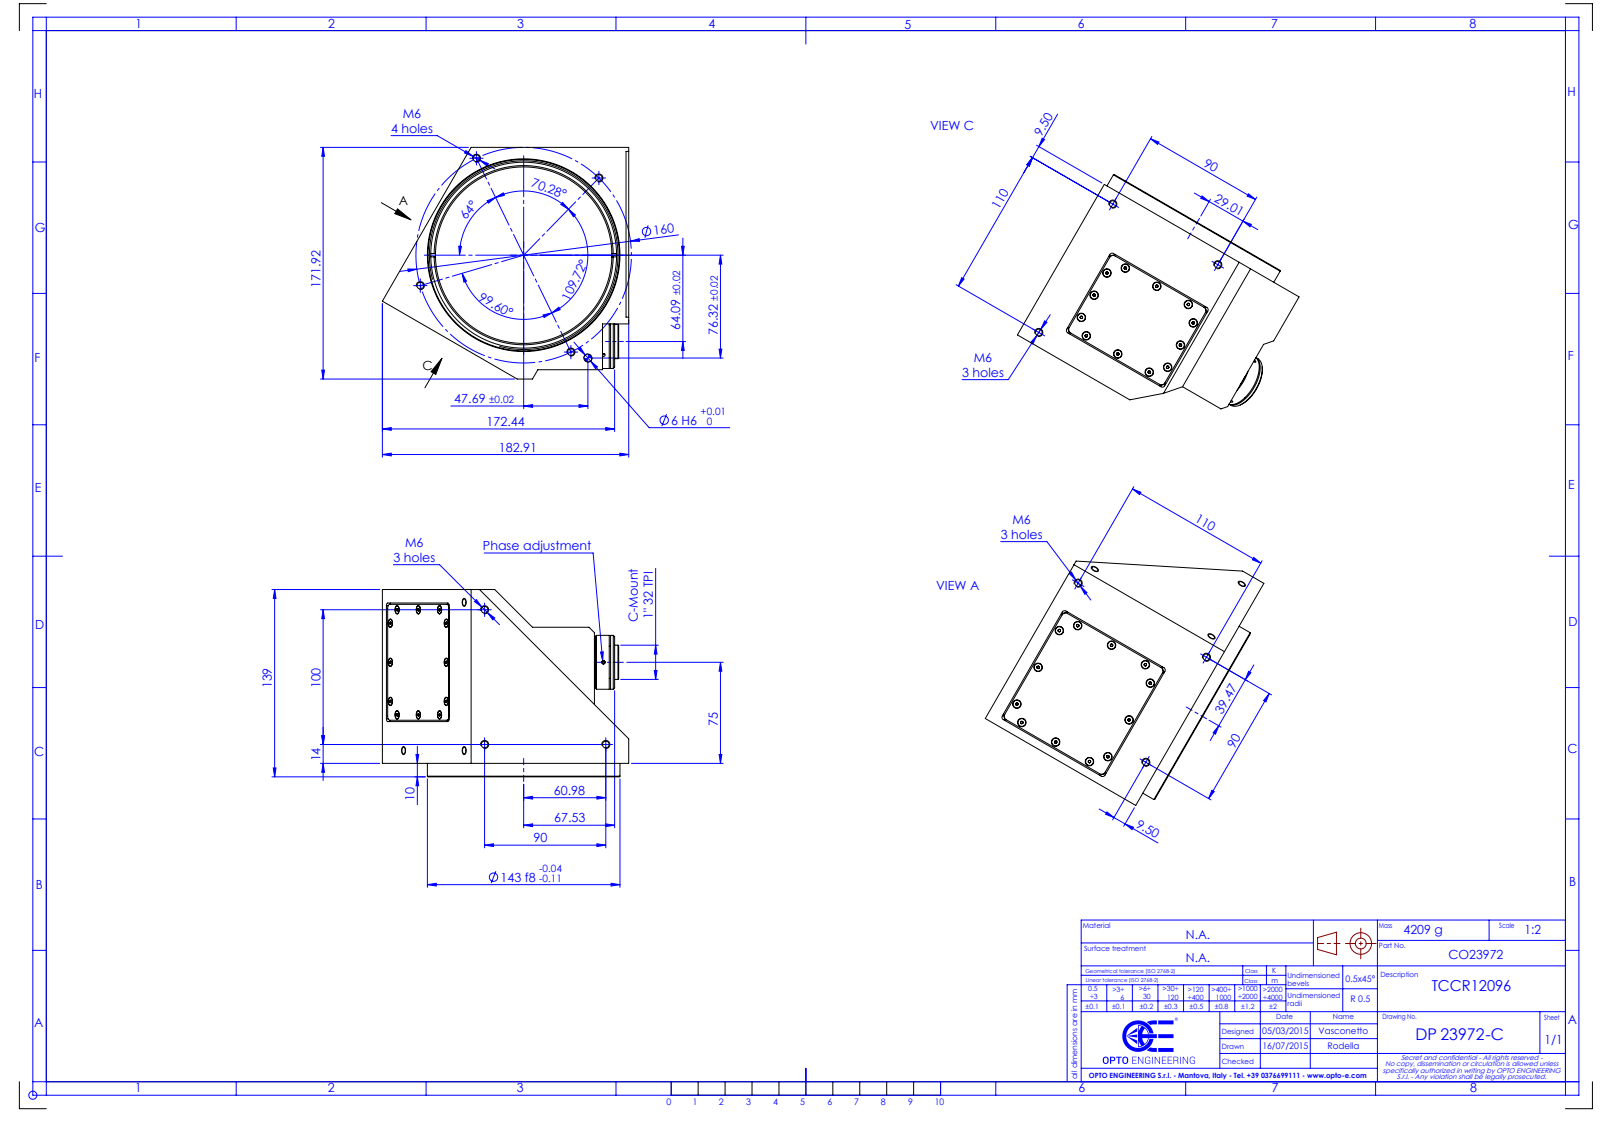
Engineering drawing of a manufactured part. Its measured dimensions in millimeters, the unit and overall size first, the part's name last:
Units: millimetres
Overall size (bounding box): 182.91 × 171.92 × 139
Round holes (diameter × count): ⌀5 ×13, ⌀2.5 ×3, ⌀1.8 ×2, ⌀6 ×1, ⌀14.5 ×1, ⌀22 ×1, ⌀22.5 ×1, ⌀131 ×1, ⌀138 ×1
Round bosses / shafts (diameter × count): ⌀5.75 ×30, ⌀143 ×1, ⌀40 ×1, ⌀38.2 ×1, ⌀37.8 ×1, ⌀25.4 ×1
Partial cylindrical surfaces — rounded edges, fillets, slot ends (radius × count): R2 ×8, R3 ×8, R4 ×2
Main face-to-face distances: 0.5, 129, 165, 8, 39, 6, 10, 126, 109, 1
Hole centre spacings: 80, 90, 10, 110, 142.13, 13.37, 20, 61.03
Bodies: 0 solids, 482 faces (208 planar, 138 cylindrical, 136 other)
Part name (STEP PRODUCT): DP23972_TCCR12096
STEP written by: SolidWorks 2021 (CONFIG_CONTROL_DESIGN)
